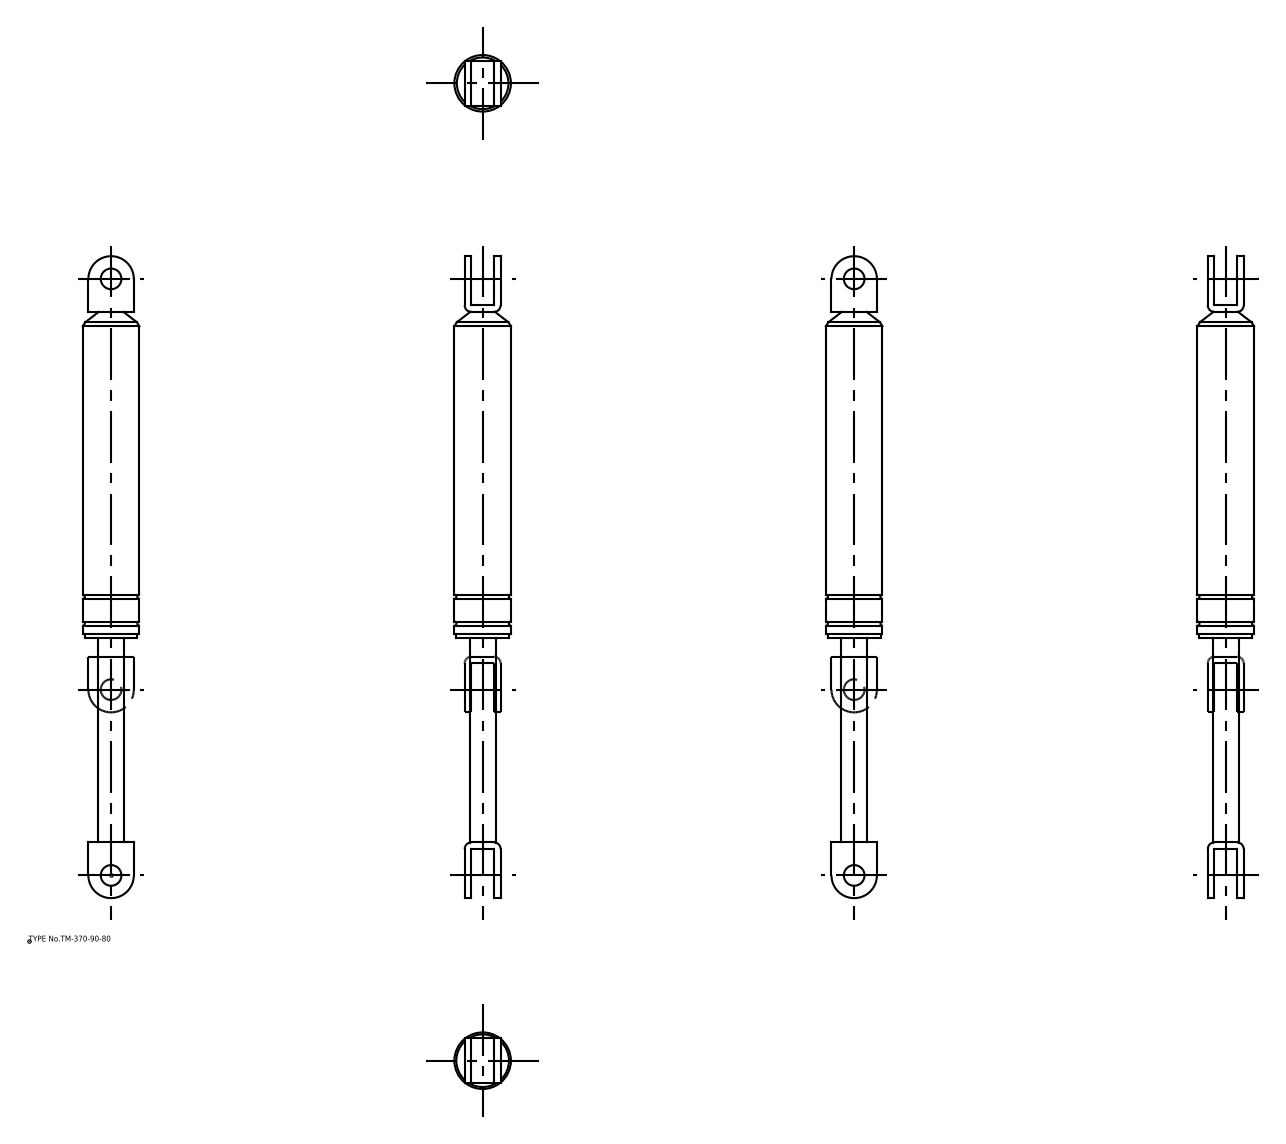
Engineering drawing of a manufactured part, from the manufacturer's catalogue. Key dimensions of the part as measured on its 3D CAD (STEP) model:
Part name (STEP PRODUCT): TM_370_90_80; TM_370_90_80_div
STEP written by: spGate 16.7.1 (AUTOMOTIVE_DESIGN)
Units: millimetres
Bodies: 2 solids, 64 faces (22 planar, 32 cylindrical, 10 other)
Overall size (bounding box): 311 × 28.2 × 28.2
Volume: 110 999 mm³ · Surface area: 24 270 mm²
Round holes (diameter × count): ⌀10 ×2
Round bosses / shafts (diameter × count): ⌀28.2 ×1, ⌀27.4 ×1, ⌀25.5 ×1, ⌀12.5 ×1
Partial cylindrical surfaces — rounded edges, fillets, slot ends (radius × count): R3.2 ×4, R11 ×2
Main face-to-face distances: 3.2, 14.2, 17.4, 11, 22, 260.2, 102.2, 263.4, 161.2, 158
Hole centre spacings: 289
